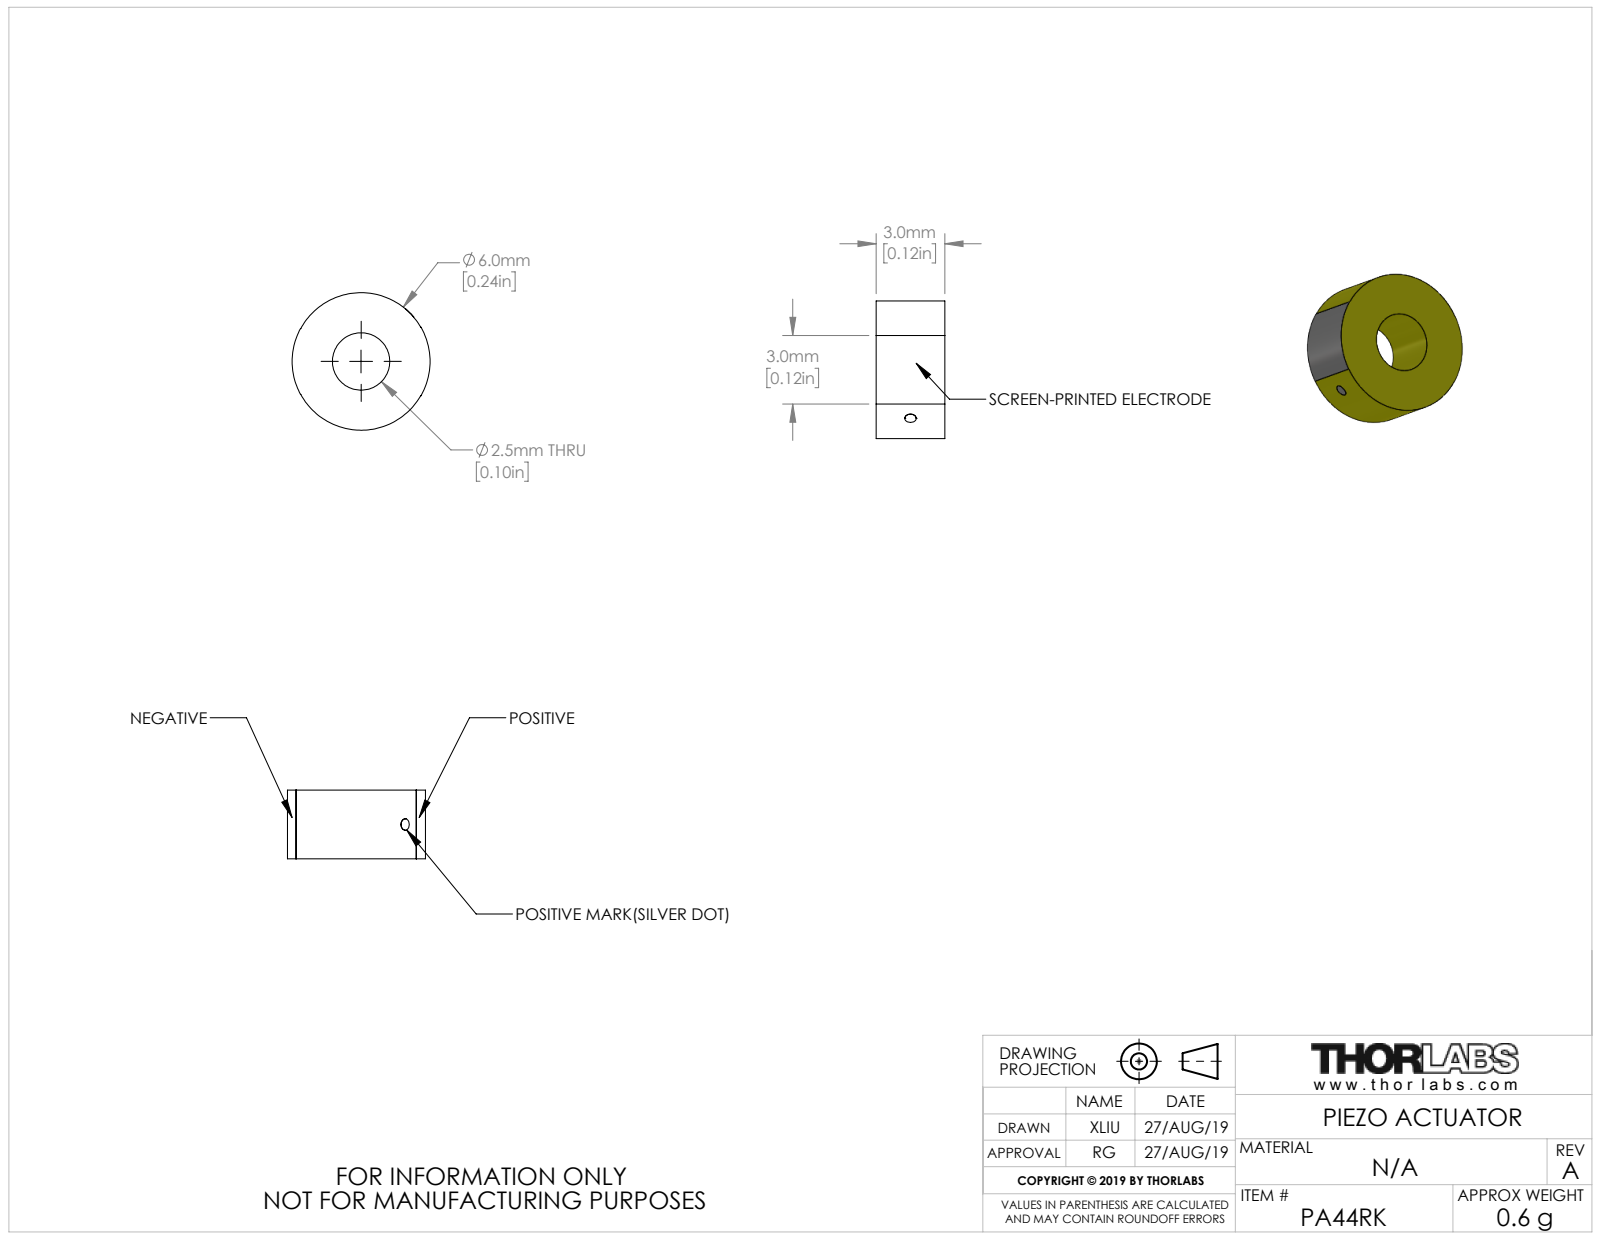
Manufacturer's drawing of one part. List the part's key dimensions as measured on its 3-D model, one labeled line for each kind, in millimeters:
Part name (STEP PRODUCT): CTN014424
STEP written by: SolidWorks 2018 (AUTOMOTIVE_DESIGN)
Units: millimetres
Bodies: 1 solid, 16 faces (5 planar, 8 cylindrical, 3 other)
Overall size (bounding box): 6.02 × 6 × 3
Volume: 70 mm³ · Surface area: 127 mm²
Round holes (diameter × count): ⌀2.5 ×1
Partial cylindrical surfaces — rounded edges, fillets, slot ends (radius × count): R3 ×1, R3.01 ×1
Main face-to-face distances: 3
